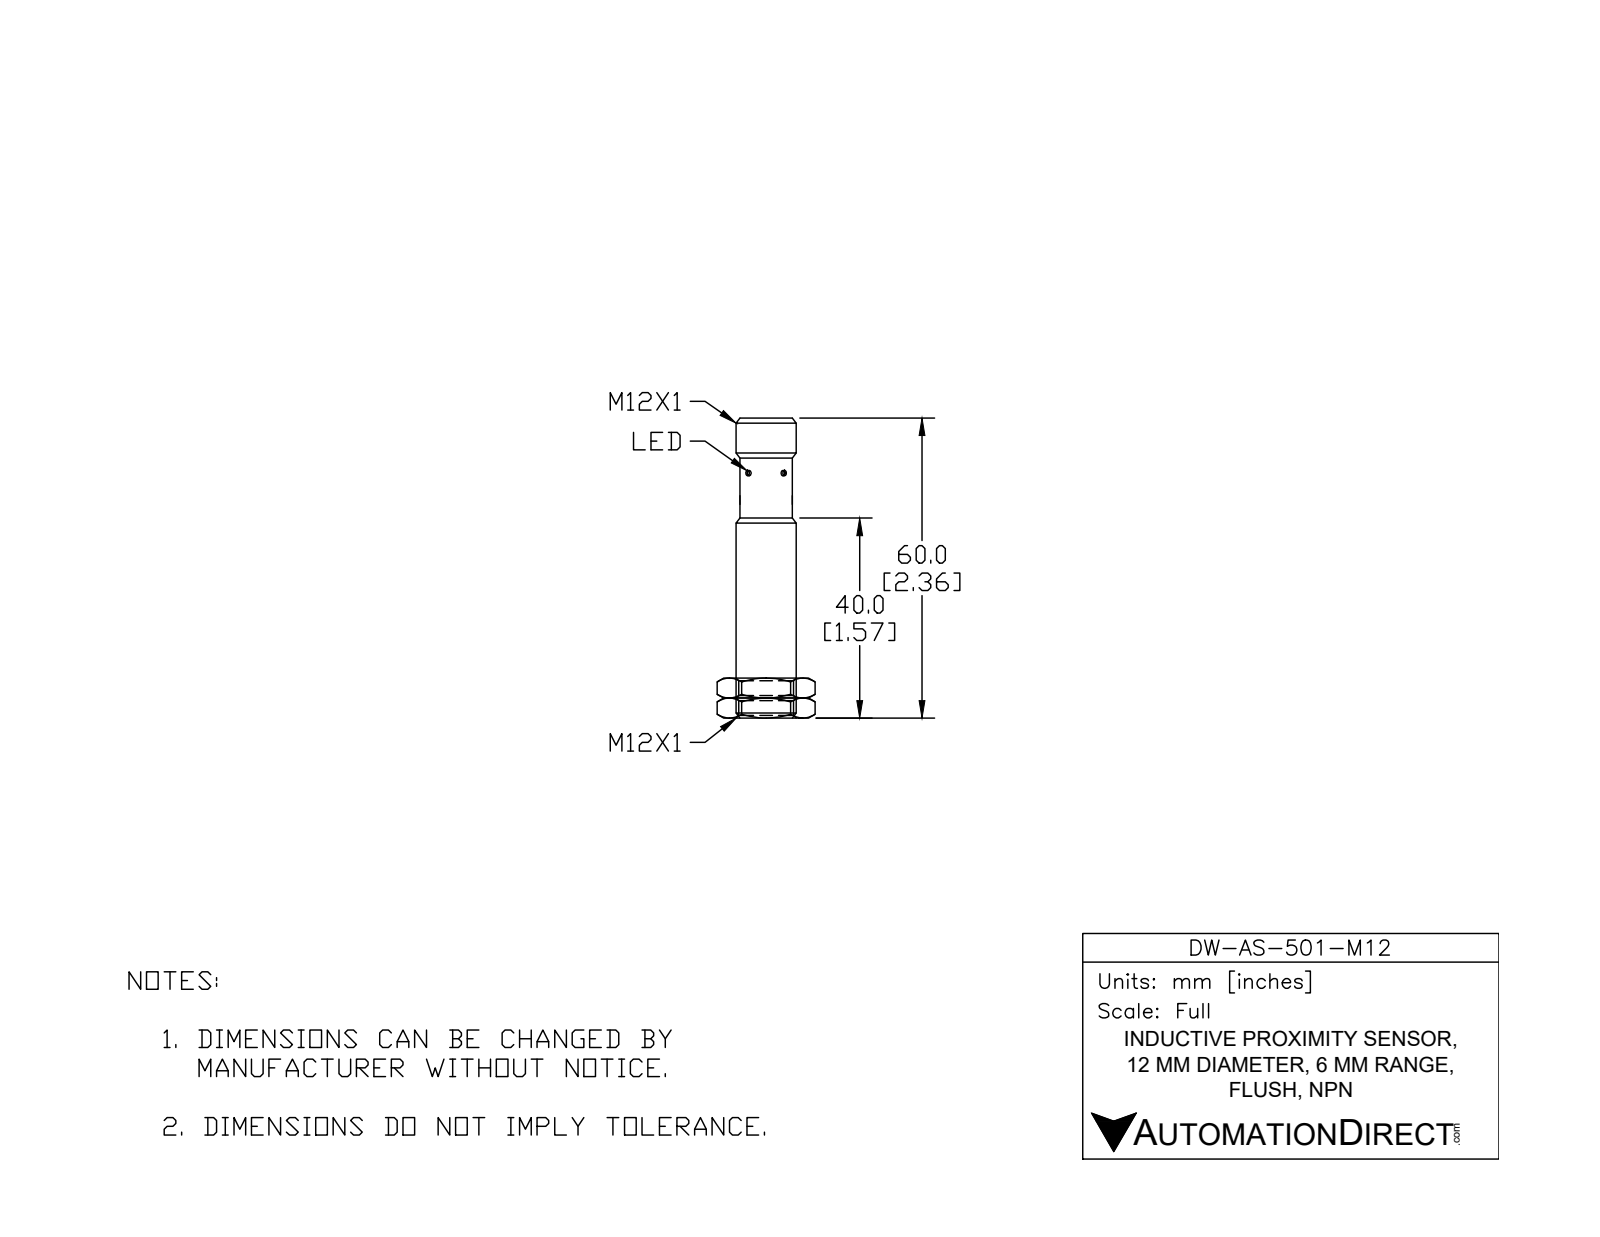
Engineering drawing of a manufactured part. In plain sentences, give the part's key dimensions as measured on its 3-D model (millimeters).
The part is named "DW-AD-501-M12". Its 3-D file was written by "SolidWorks 2017 (AUTOMOTIVE_DESIGN)". It is 2 solids with 42 faces: 18 planar, 7 cylindrical and 17 other. Overall it measures 75.6 by 12 by 12 millimeters. Its volume is 6 290 cubic millimeters and its surface area 2 620 square millimeters. Round bosses or shafts: 1 of diameter 12, 1 of diameter 10.5, 1 of diameter 6.8, 1 of diameter 5. The main face-to-face distances are 51.8, 50.6, 1.2, 46.8, 3.8, 5, 51.4, 4.6, 0.8, 0.4.
